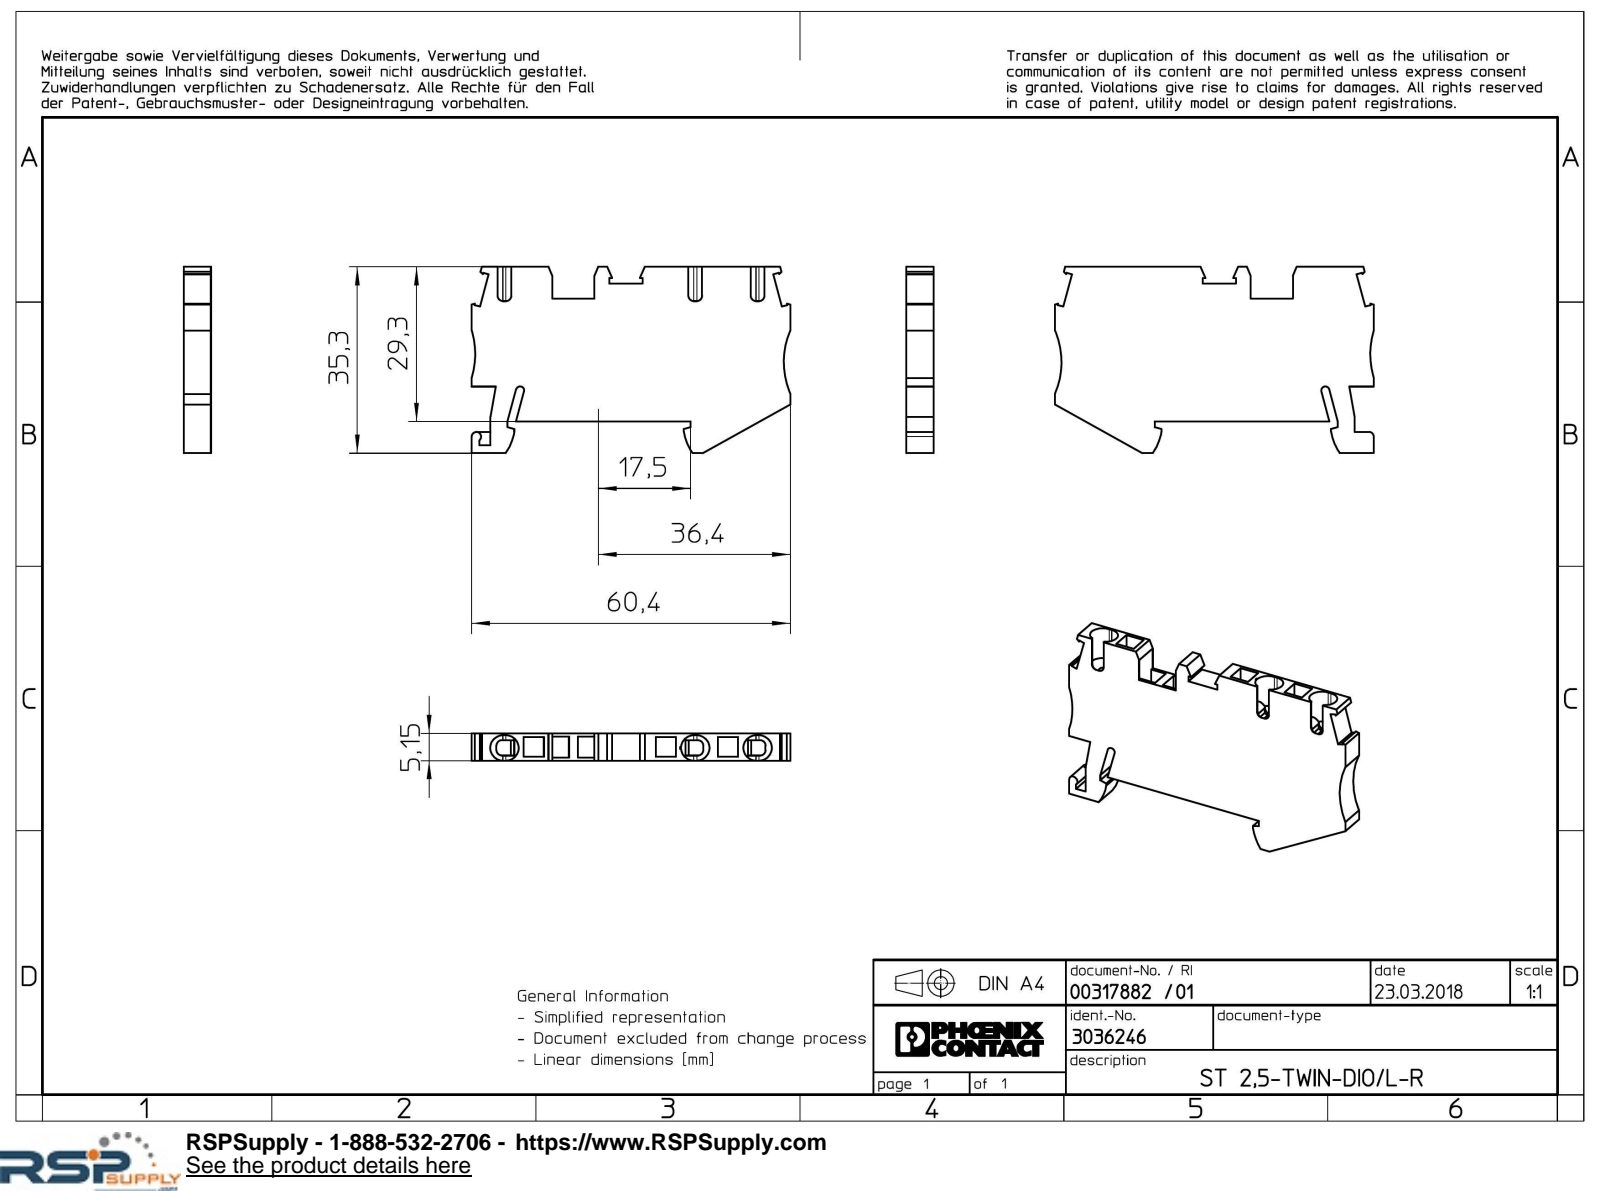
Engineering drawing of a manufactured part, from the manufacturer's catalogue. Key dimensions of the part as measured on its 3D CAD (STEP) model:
Part name (STEP PRODUCT): ST25-TWIN-DIO_L-R_Select
STEP written by: Creo Elements/Direct Modeling 20.1A 29-Sep-2018 (C) Parametric Technology GmbH (AUTOMOTIVE_DESIGN)
Units: millimetres
Bodies: 1 solid, 160 faces (125 planar, 25 cylindrical, 10 other)
Overall size (bounding box): 60.4 × 35.25 × 5.15
Volume: 7 453 mm³ · Surface area: 5 800 mm²
Partial cylindrical surfaces — rounded edges, fillets, slot ends (radius × count): R1 ×12, R2.4 ×6, R9.5 ×2, R15 ×2, R0.7 ×1, R0.8 ×1, R0.9 ×1
Main face-to-face distances: 5.15, 3.15, 3.8, 0.65, 29.25, 4.85, 4.45, 8, 3.85, 4
